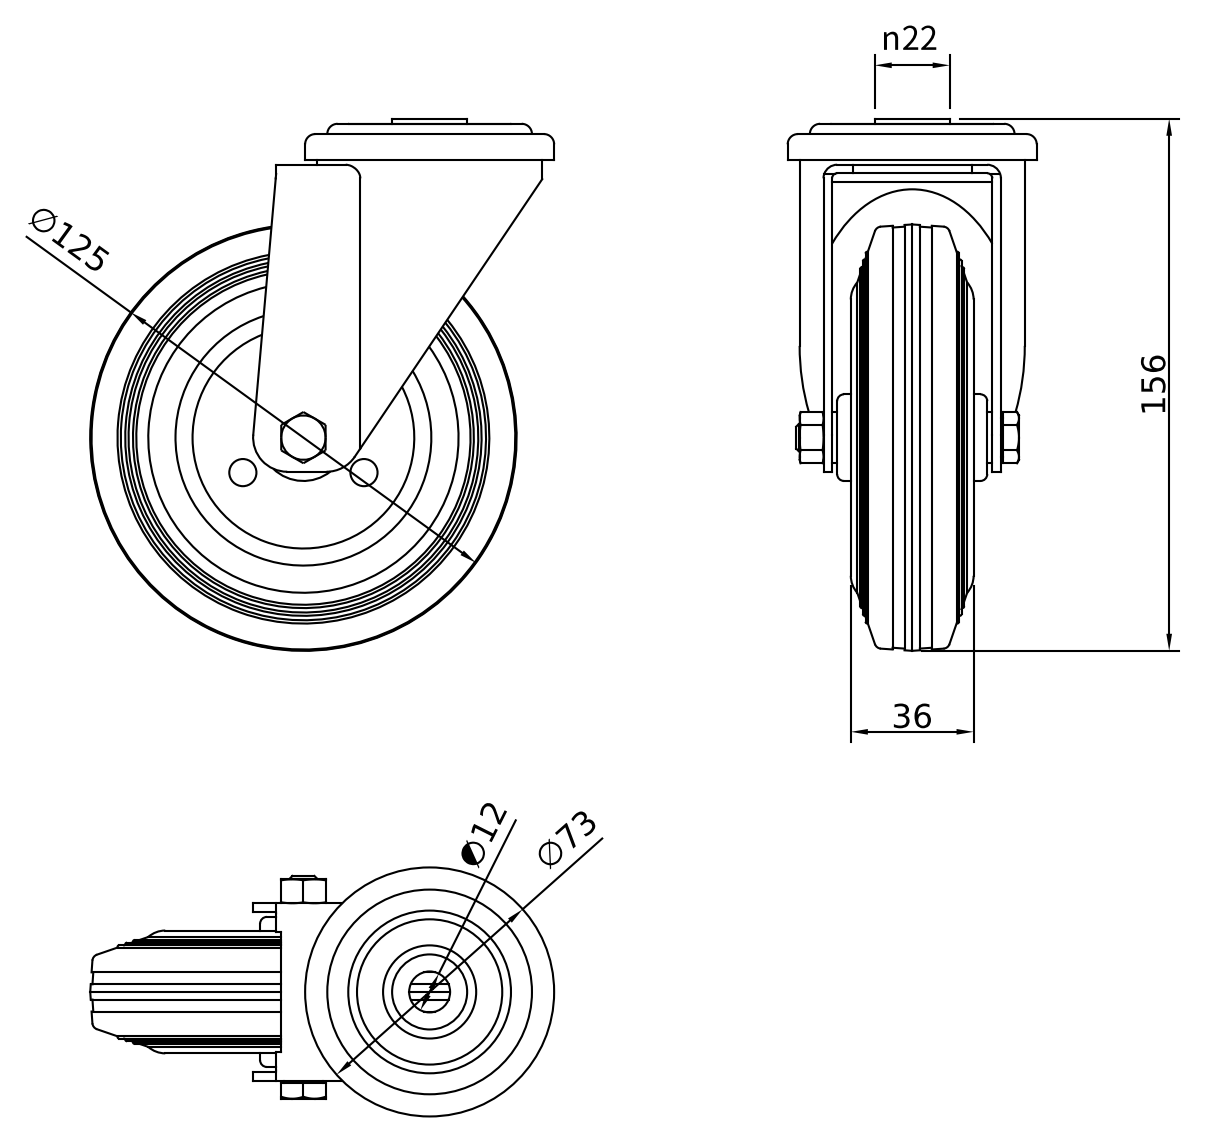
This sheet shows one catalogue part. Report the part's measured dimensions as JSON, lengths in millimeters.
{"part_name": "CRUST0000184; 440000025367; 440000025368; 440000025369 (+2 more)", "step_written_by": "Autodesk Inventor 2022 (AUTOMOTIVE_DESIGN)", "units": "millimeters", "bodies": {"solids": 5, "faces": 155, "planar": 58, "cylindrical": 32, "other": 65}, "overall_size": [156, 136, 73], "volume_mm3": 380064, "surface_area_mm2": 85699, "round_holes": [[6.65, 1], [8, 1], [12, 1], [15, 1], [15.5, 1], [18, 1], [62, 1], [65, 1]], "round_bosses_or_shafts": [[75, 1], [73, 1], [66, 1], [54, 1], [25.4, 1], [22, 1], [11.47, 1]], "partial_cylinders_radius": [[1.5, 2], [4, 2], [10, 2]], "face_to_face_distances": [2.5, 49.5, 24.8, 27.2, 22.3, 24.7, 47, 52, 1.5, 4]}
